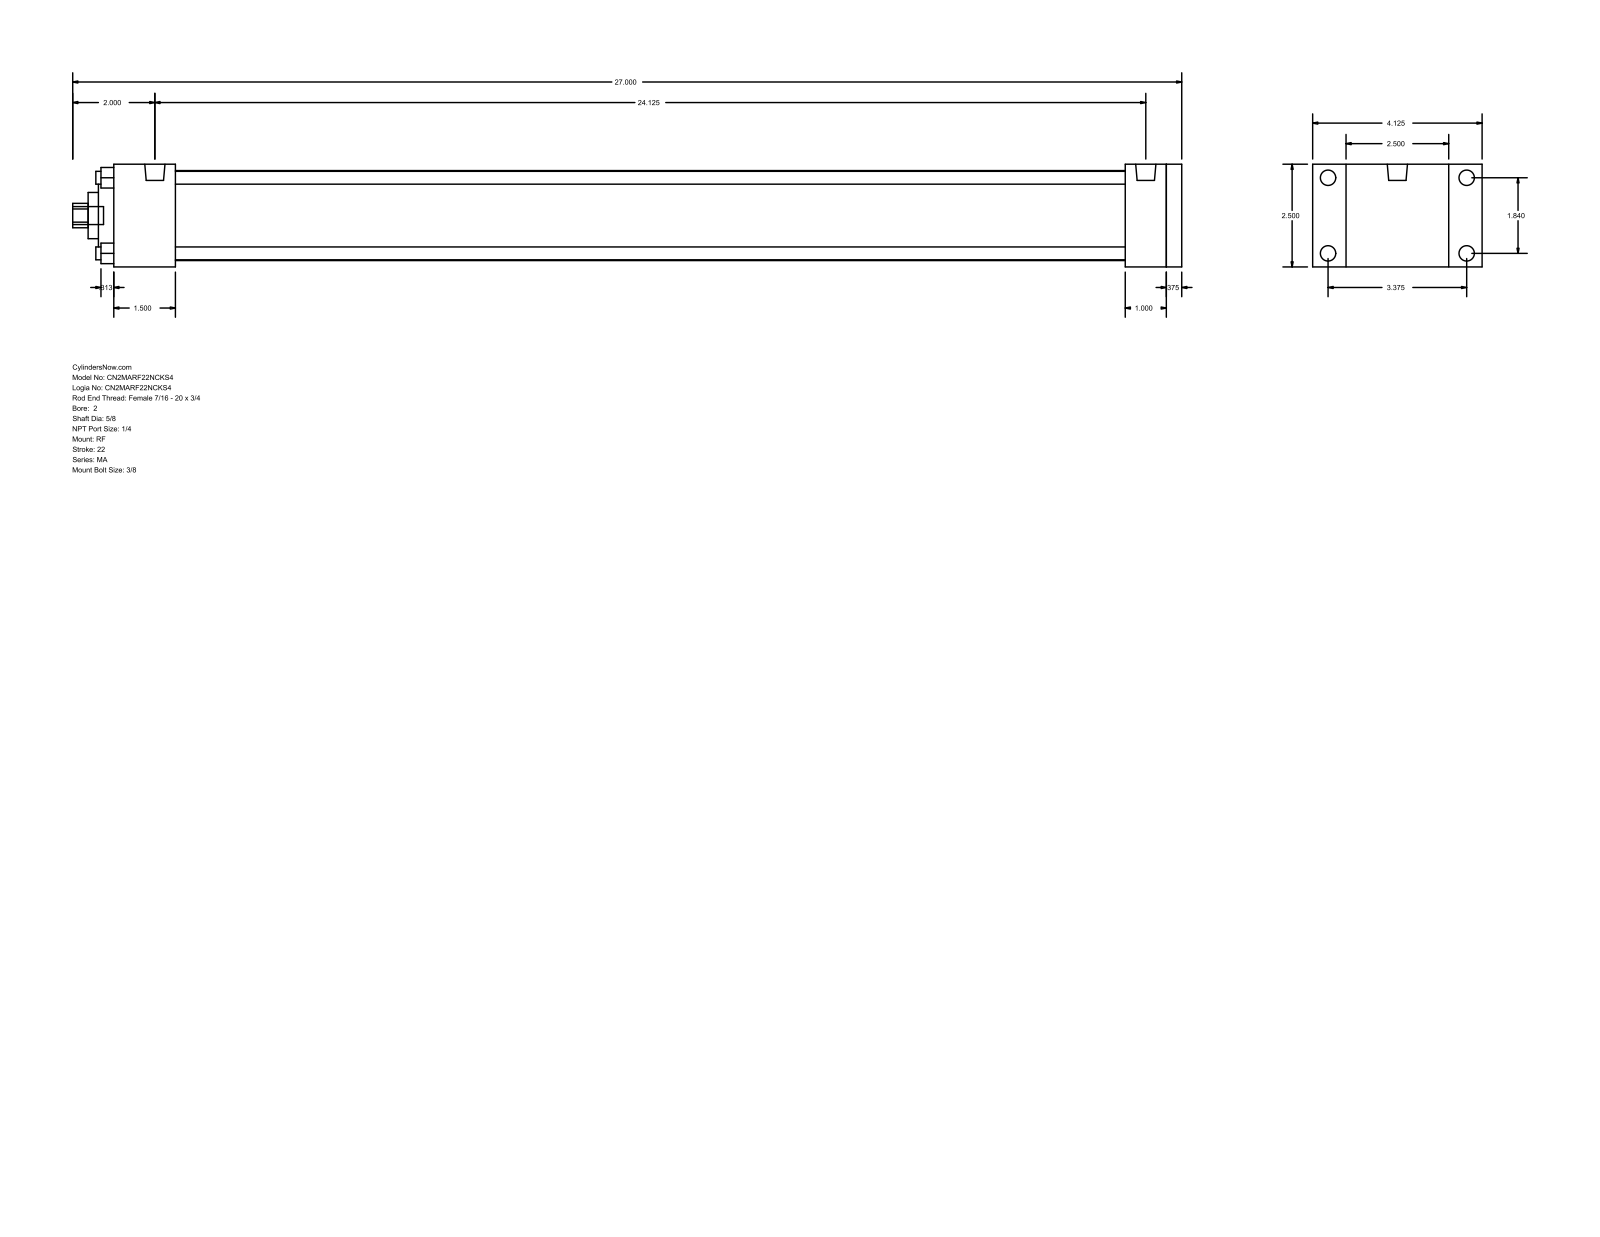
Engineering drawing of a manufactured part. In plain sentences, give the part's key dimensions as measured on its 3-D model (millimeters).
The part is named "MA_RF__0200_0.625". Its 3-D file was written by "GSSL Pune (CONFIG_CONTROL_DESIGN)". It is 0 solids with 94 faces: 65 planar, 29 cylindrical and 0 other. Overall it measures 685.8 by 104.78 by 63.5 millimeters. Round holes: 4 of diameter 7.94, 1 of diameter 15.88, 1 of diameter 28.57, 1 of diameter 50.8, 1 of diameter 55.63. Round bosses or shafts: 4 of diameter 9.53, 4 of diameter 7.94, 2 of diameter 12.49, 1 of diameter 11.11. Partial cylindrical surfaces (rounded edges, fillets, slot ends): 1 of radius 7.54. The main face-to-face distances are 63.5, 9.53, 38.1, 9.52, 650.87, 660.4, 669.92, 612.77, 622.3, 625.48. The hole center spacings are 33.05, 46.74, 66.1.
